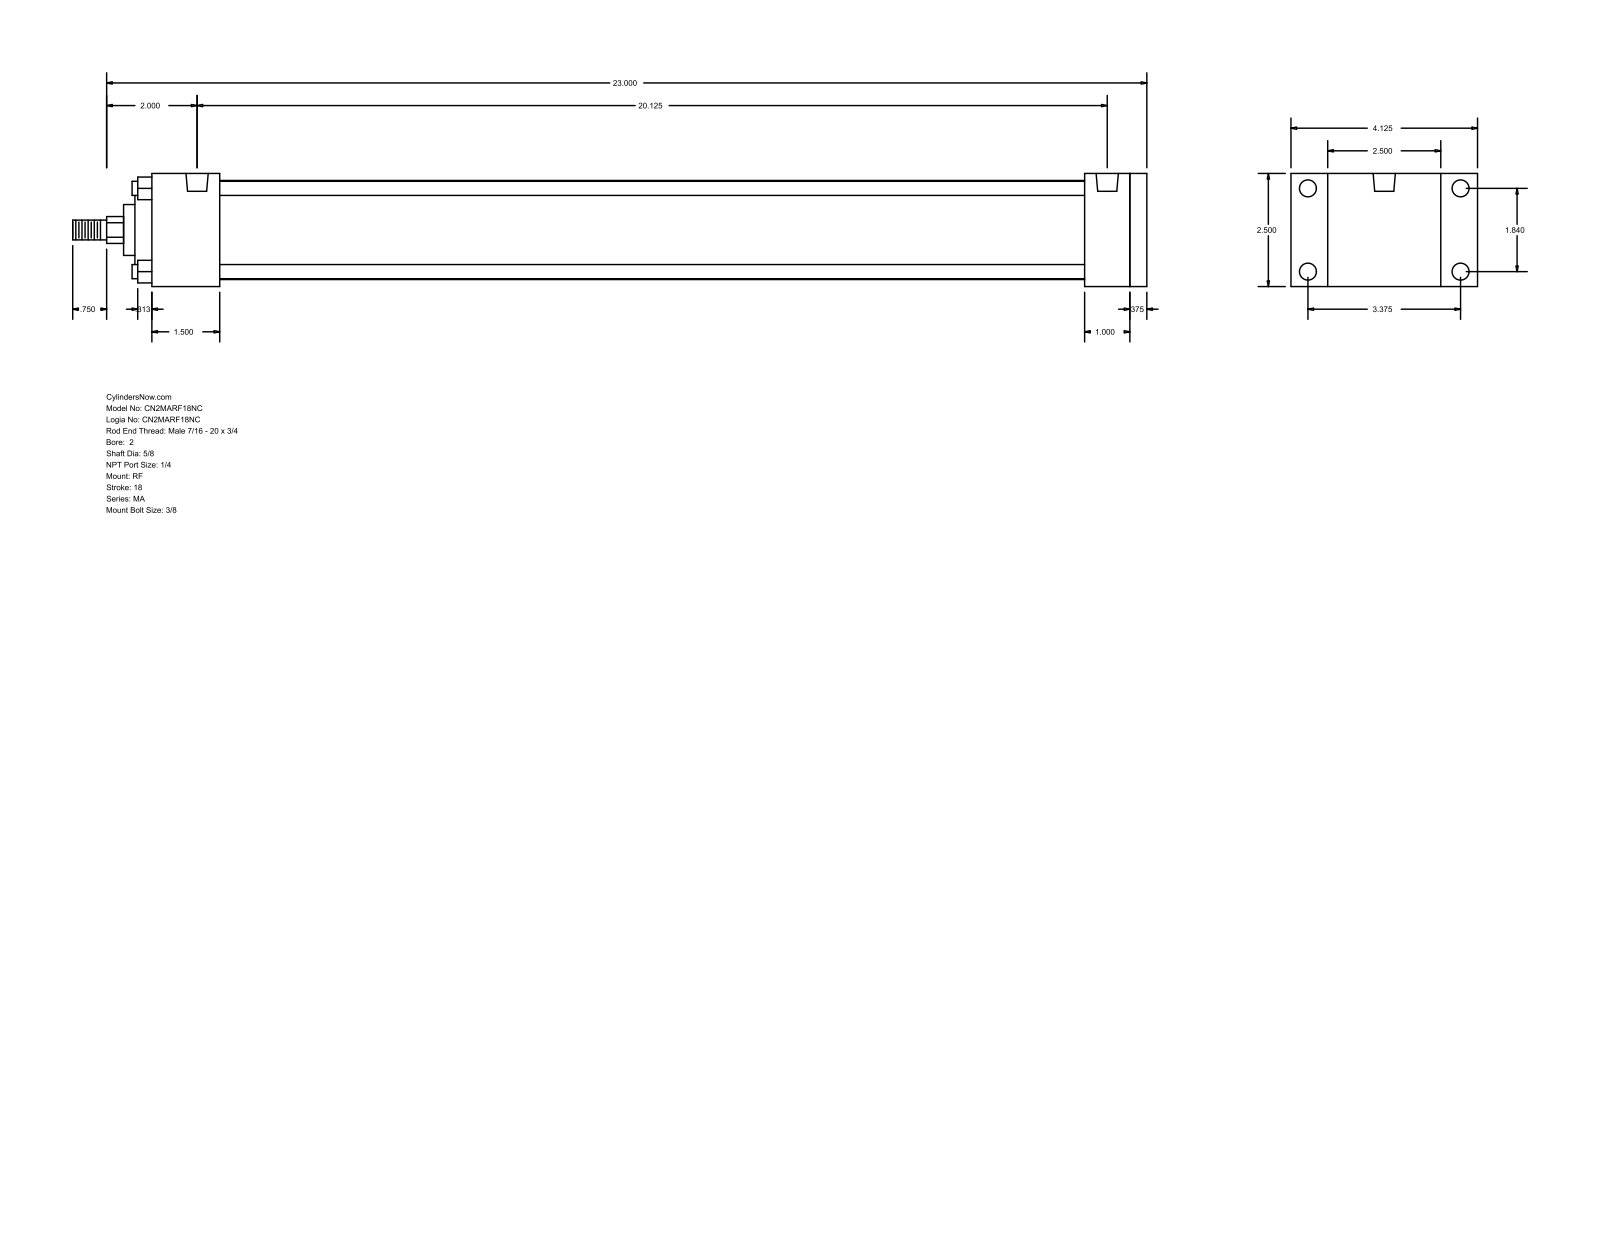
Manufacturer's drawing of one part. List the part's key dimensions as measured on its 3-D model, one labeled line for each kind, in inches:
Part name (STEP PRODUCT): MA_RF__0200_0.625
STEP written by: GSSL Pune (CONFIG_CONTROL_DESIGN)
Units: inches
Bodies: 0 solids, 94 faces (65 planar, 29 cylindrical, 0 other)
Overall size (bounding box): 23.75 × 4.125 × 2.5
Round holes (diameter × count): ⌀0.313 ×4, ⌀0.375 ×4, ⌀0.492 ×2
Round bosses / shafts (diameter × count): ⌀0.313 ×4, ⌀2.19 ×1, ⌀2 ×1, ⌀1.125 ×1, ⌀0.625 ×1, ⌀0.437 ×1
Partial cylindrical surfaces — rounded edges, fillets, slot ends (radius × count): R0.297 ×1
Main face-to-face distances: 2.5, 0.375, 1, 1.5, 22.375, 21.625, 1.375, 22, 20.125, 20.5
Hole centre spacings: 1.84, 3.375, 3.844, 20.125
